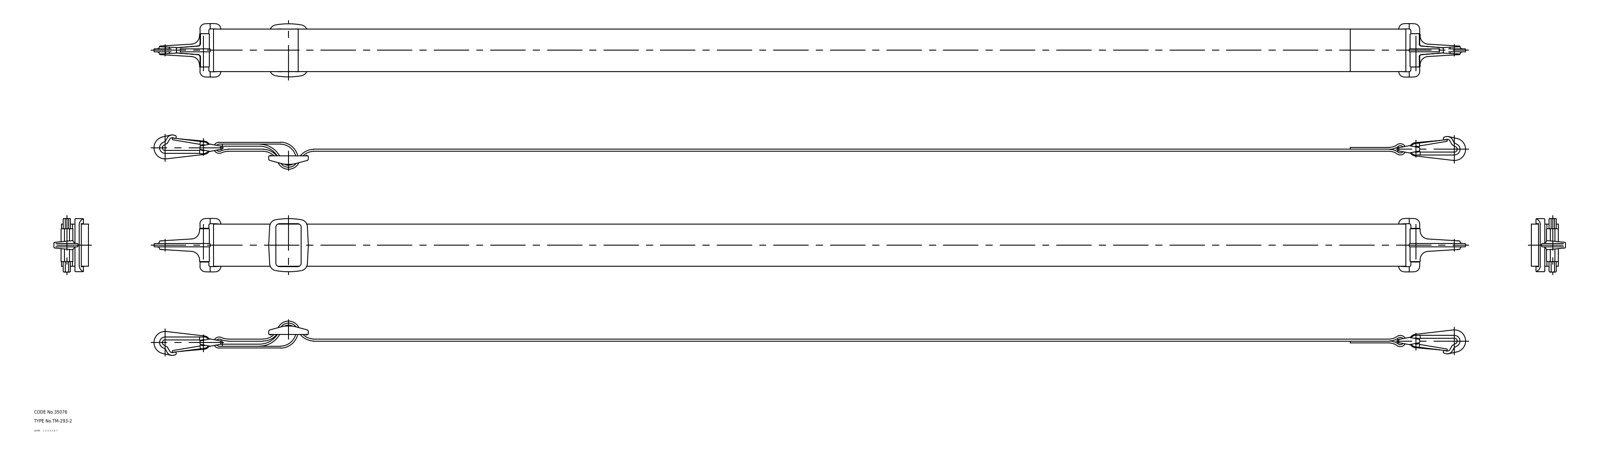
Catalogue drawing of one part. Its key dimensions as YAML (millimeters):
part_name: "67147819; 67147832; 67147845; 67147858"
step_written_by: "CADfix (AUTOMOTIVE_DESIGN)"
units: millimeters
bodies: {solids: 2, faces: 692, planar: 0, cylindrical: 0, other: 692}
overall_size: [1177.05, 48, 30.81]
volume: 93141
surface_area: 116528
